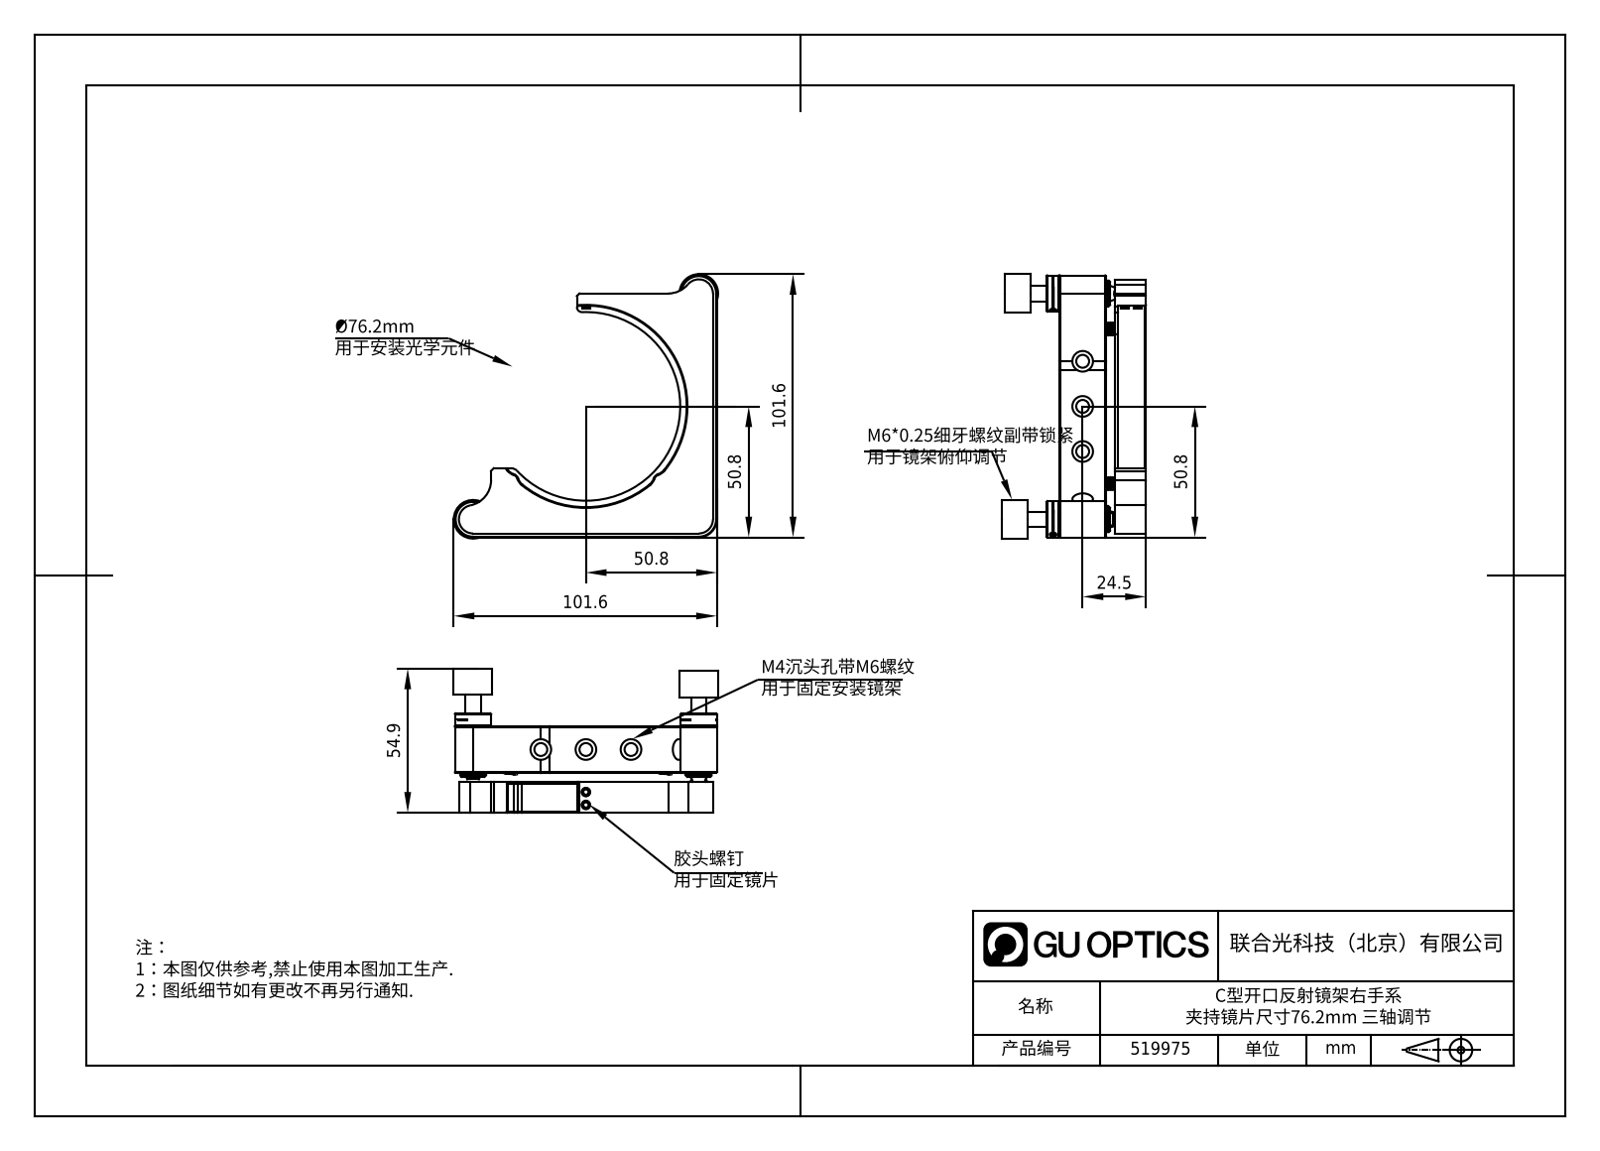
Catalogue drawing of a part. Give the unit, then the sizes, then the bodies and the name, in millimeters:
Units: millimetres
Overall size (bounding box): 101.6 × 101.6 × 50.5
Round holes (diameter × count): ⌀9.5 ×3, ⌀10 ×3, ⌀14 ×3
Round bosses / shafts (diameter × count): ⌀4 ×8, ⌀6 ×7, ⌀10 ×6, ⌀5 ×6, ⌀2 ×4, ⌀1.5 ×4, ⌀10.5 ×3, ⌀8 ×3
Partial cylindrical surfaces — rounded edges, fillets, slot ends (radius × count): R1.1 ×8, R2.5 ×7, R0.8 ×4, R1.25 ×4, R1.5 ×4, R3.5 ×4, R6 ×4, R5.25 ×3
Main face-to-face distances: 12, 33.5, 21.5, 15.5, 3.5, 18, 2, 14, 2.25, 2.75
Hole centre spacings: 87.6, 123.89
Bodies: 0 solids, 1107 faces (648 planar, 325 cylindrical, 134 other)
Part name (STEP PRODUCT): 519975
STEP written by: SolidWorks 2020 (CONFIG_CONTROL_DESIGN)
